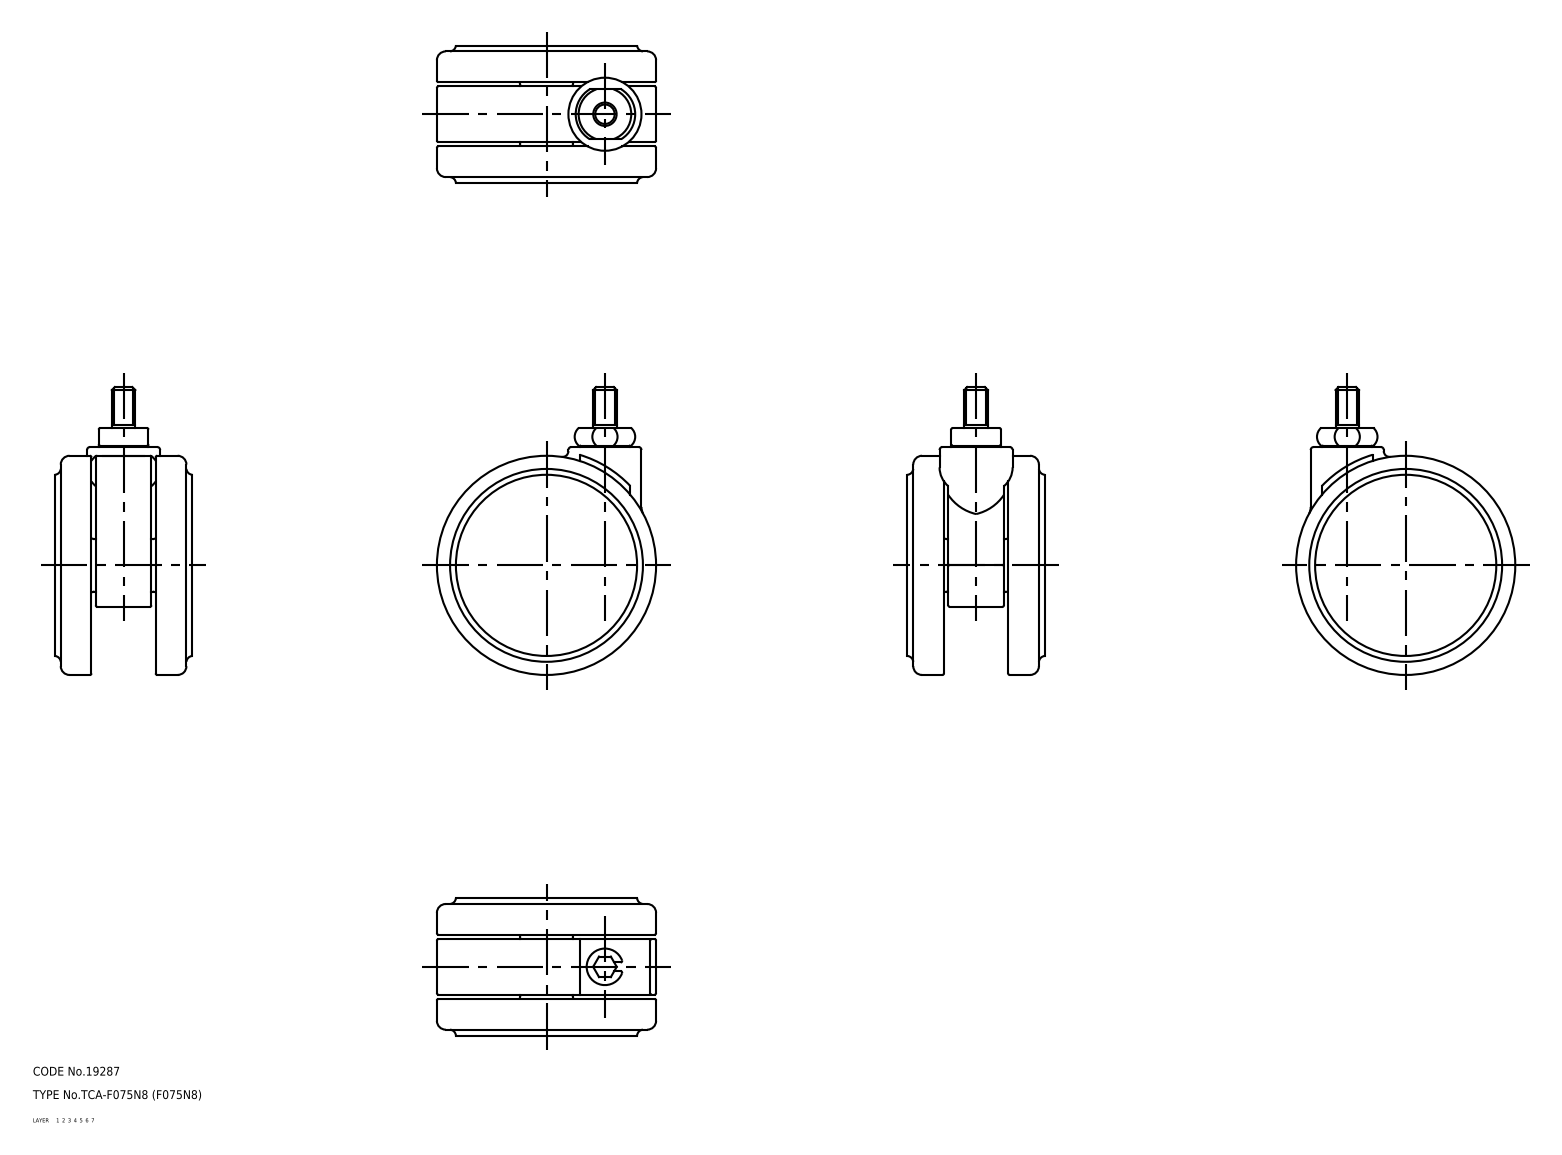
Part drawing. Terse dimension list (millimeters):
name: 67116585; 67116598; 67116611; 67116624
written by: CADfix (AUTOMOTIVE_DESIGN)
unit: mm
bodies: 4 solids, 122 faces (0 planar, 0 cylindrical, 122 other)
size: 98.5 × 75 × 47
volume: 159 665 mm³; area: 36 813 mm²
